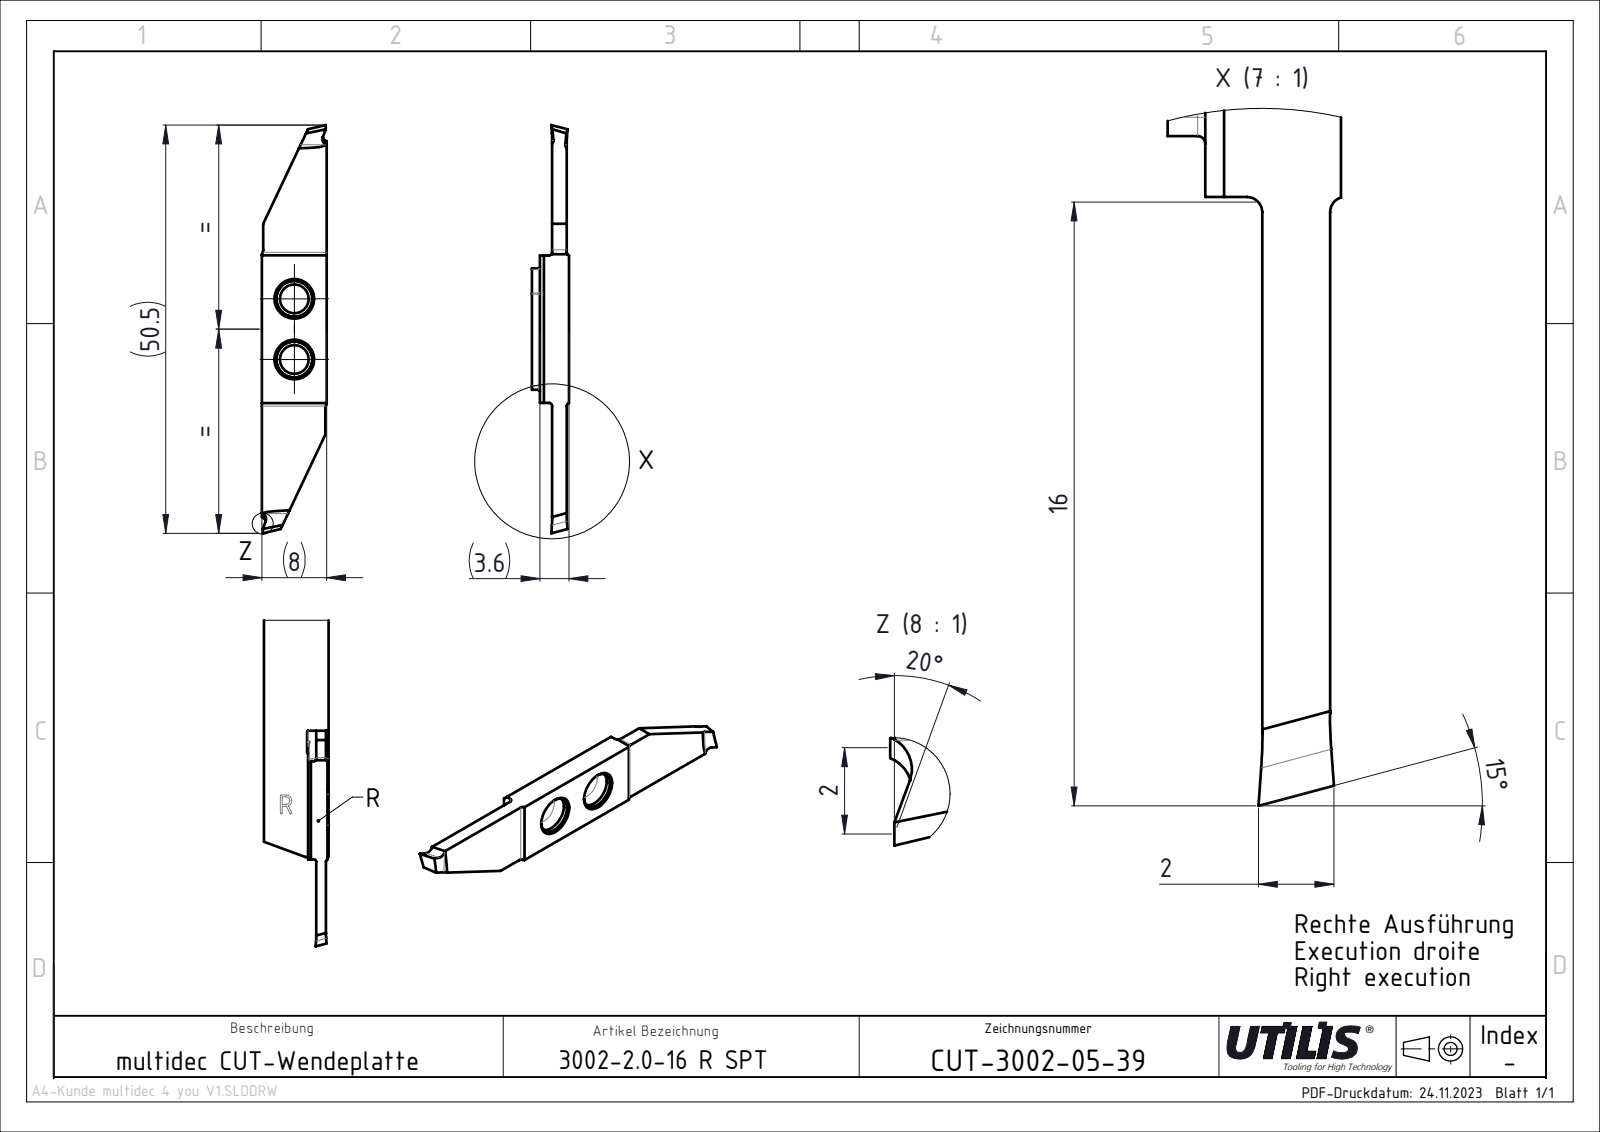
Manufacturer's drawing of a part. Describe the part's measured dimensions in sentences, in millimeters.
The part is named "CUT-3002 SPT Slim_and_Deep; ASME Y14.5". Its 3-D file was written by "SolidWorks 2023 SP4 || FormatWorks Professional (AP242_MANAGED_MODEL_BASED_3D_ENGINEERING_MIM_LF)". It is 1 solid with 32 faces: 22 planar, 10 cylindrical and 0 other. Overall it measures 50.5 by 8 by 3.6 millimeters. Its volume is 778 cubic millimeters and its surface area 968 square millimeters. Round holes: 2 of diameter 3.55. Partial cylindrical surfaces (rounded edges, fillets, slot ends): 4 of radius 0.4, 2 of radius 1. The main face-to-face distances are 1.8, 2.09, 1.51, 3.31, 3.6, 8, 18.09, 7.85, 18.22, 7.7. The hole center spacings are 7.5.
